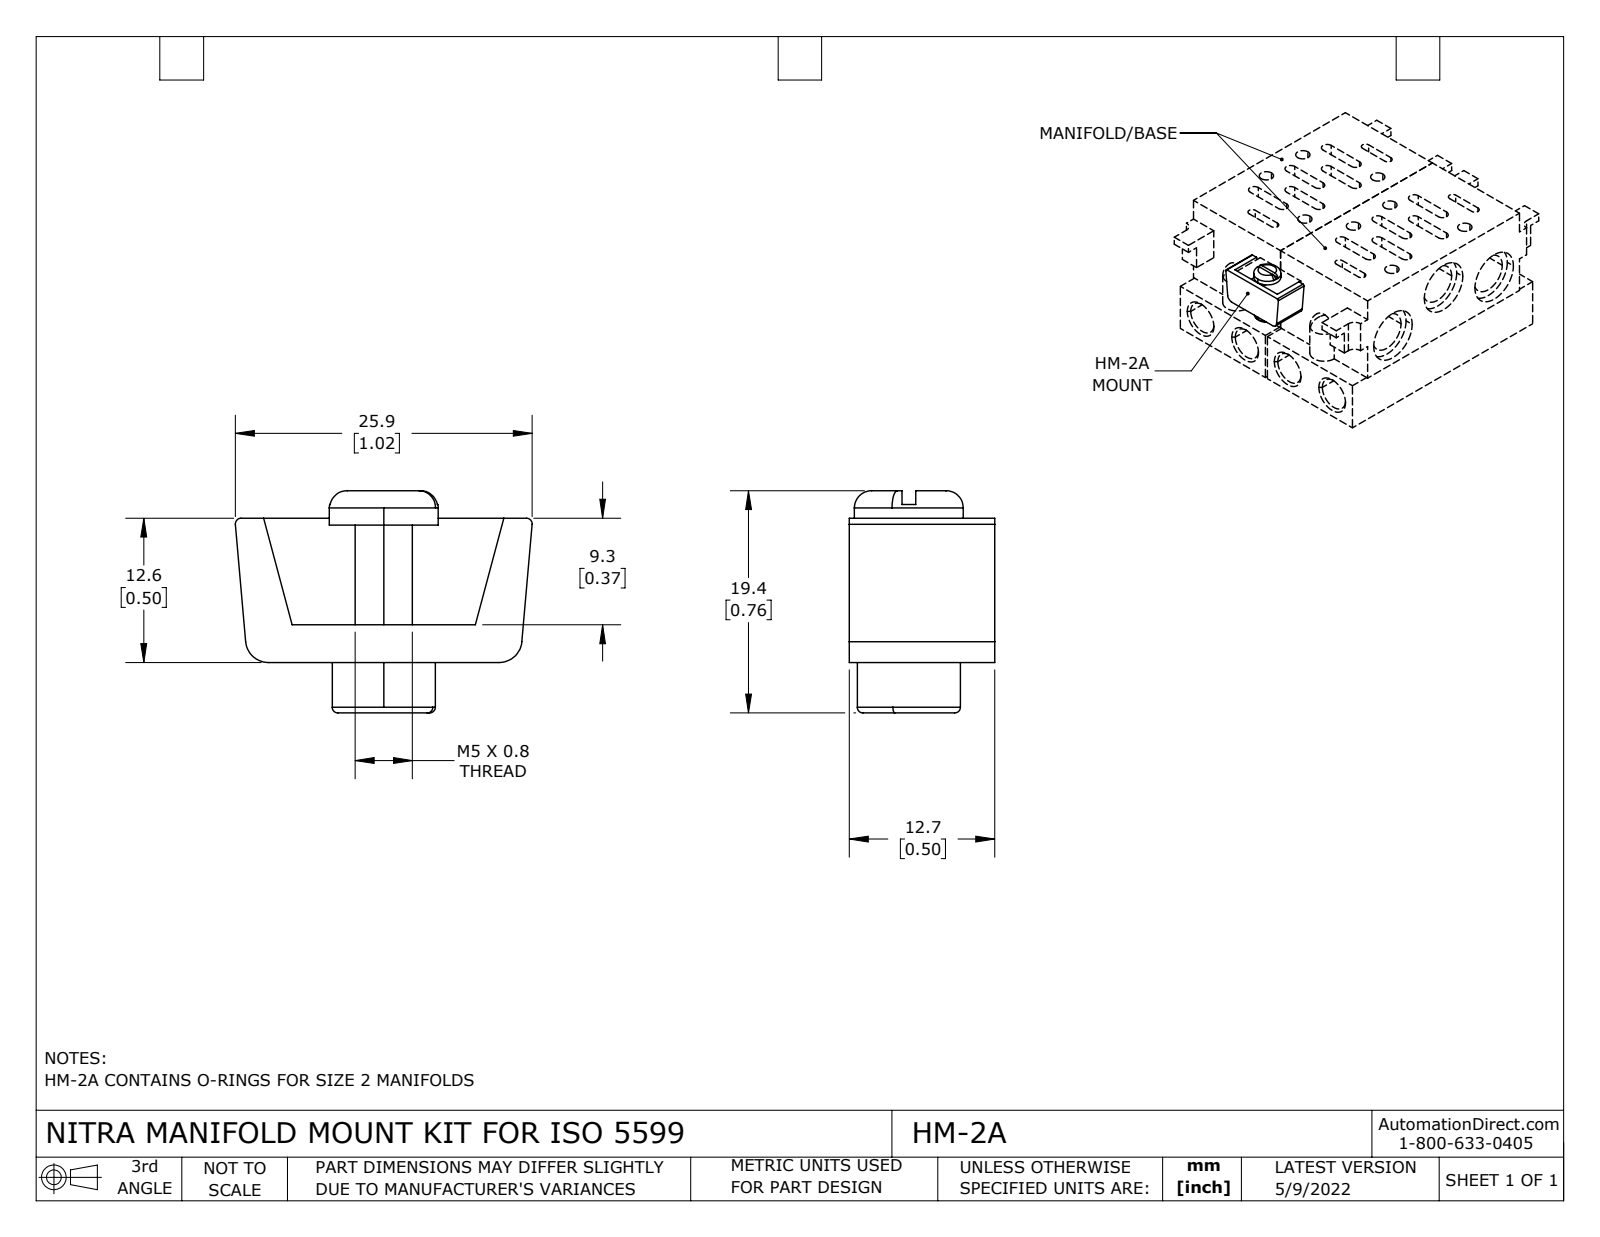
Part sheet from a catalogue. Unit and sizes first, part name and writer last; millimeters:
Units: millimetres
Overall size (bounding box): 25.91 × 19.4 × 12.7
Round holes (diameter × count): ⌀4.13 ×1
Round bosses / shafts (diameter × count): ⌀9.5 ×1, ⌀9 ×1, ⌀5 ×1
Partial cylindrical surfaces — rounded edges, fillets, slot ends (radius × count): R0.5 ×2, R2 ×2
Main face-to-face distances: 2, 3.3, 12.7, 10.7, 12.6, 9.3, 12, 8.7, 0.6, 1.2
Volume: 2 755 mm³ · Surface area: 2 156 mm²
Bodies: 1 solid, 38 faces (18 planar, 12 cylindrical, 8 other)
Part name (STEP PRODUCT): HM-2A
STEP written by: SolidWorks 2021 (CONFIG_CONTROL_DESIGN)
